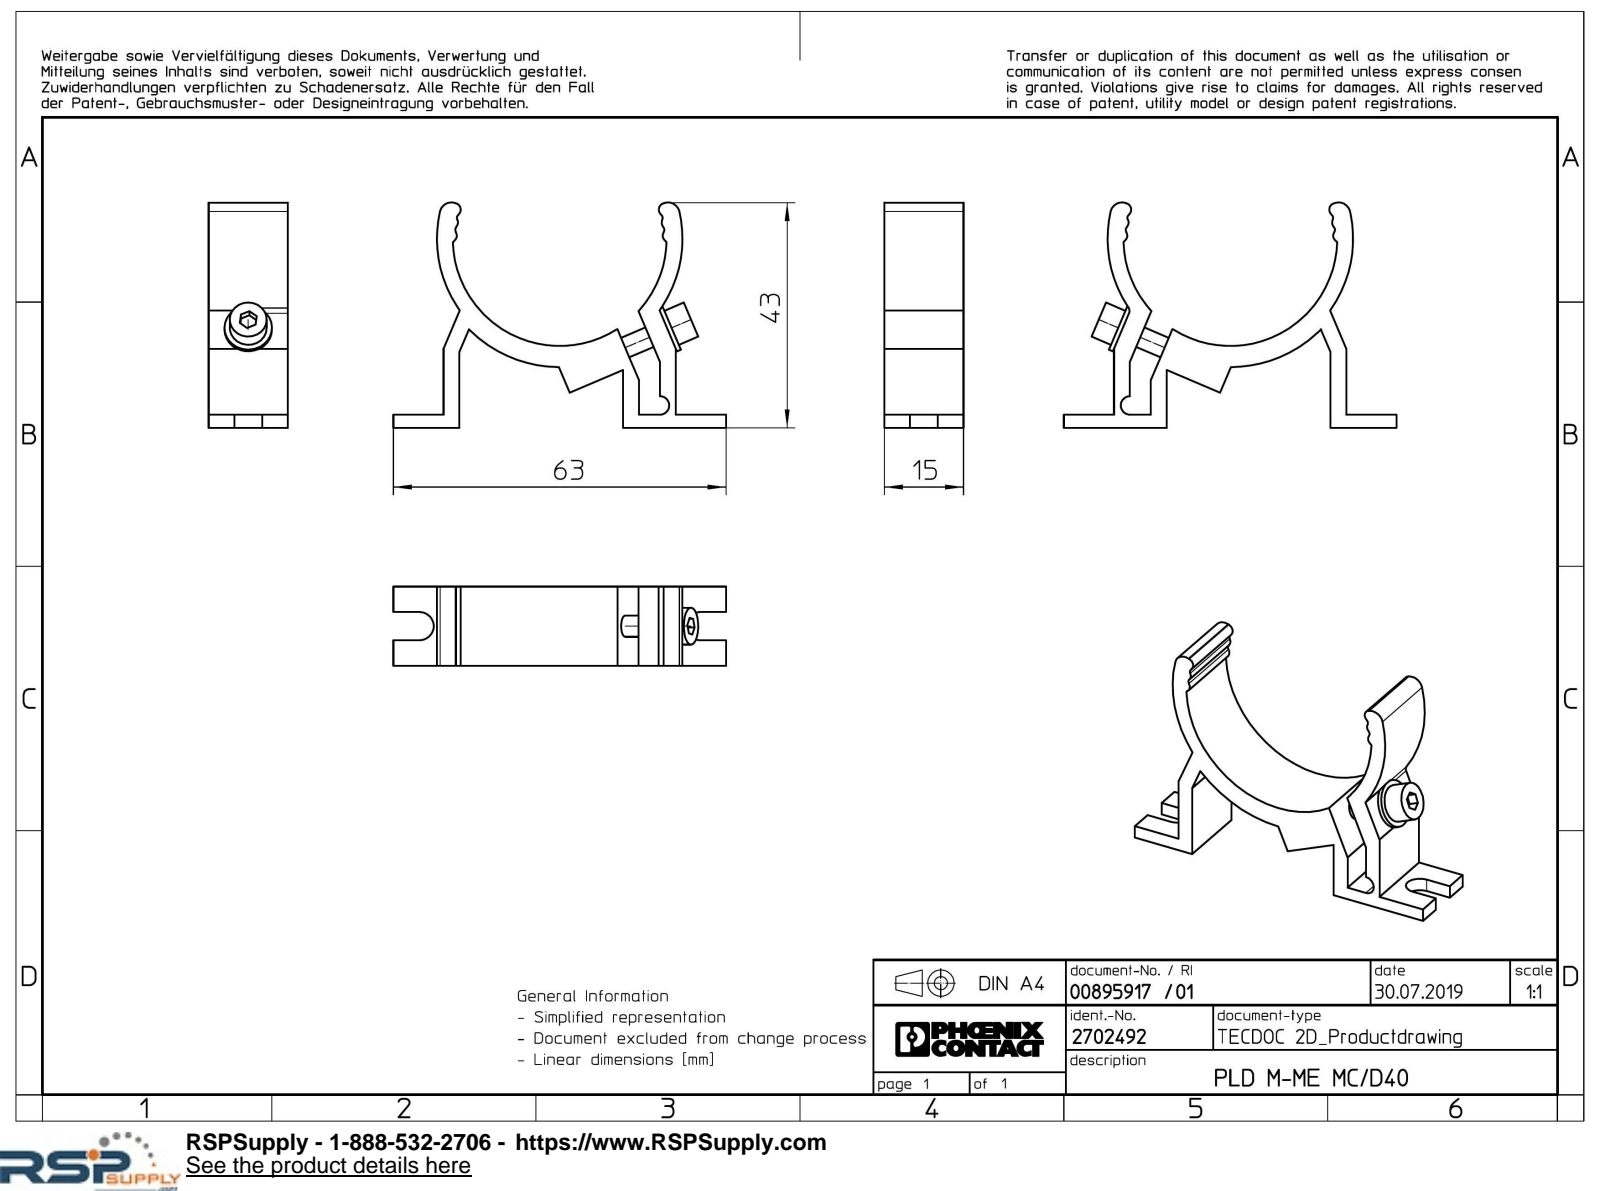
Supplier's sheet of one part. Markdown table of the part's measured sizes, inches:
| quantity | value |
| --- | --- |
| part name | PLD_M_ME_MC_D40-select |
| STEP written by | Creo Elements/Direct Modeling 20.1A 29-Sep-2018 (C) Parametric Technology GmbH (AUTOMOTIVE_DESIGN) |
| units | inches |
| bodies | 1 solid, 72 faces (42 planar, 30 cylindrical, 0 other) |
| overall size | 2.48 × 1.679 × 0.591 |
| volume | 0.495 in³ |
| surface area | 9.543 in² |
| round holes (diameter × count) | 0.185 × 1 |
| round bosses / shafts (diameter × count) | 0.354 × 1, 0.276 × 1, 0.157 × 1 |
| partial cylindrical surfaces (radius × count) | 0.049 × 6, 0.03 × 4, 0.012 × 2, 0.087 × 2, 0.104 × 2, 0.039 × 1, 0.069 × 1, 0.797 × 1 |
| main face-to-face distances | 0.591, 0.118, 1.614, 0.098, 1.339, 0.276, 1.732, 1.22, 0.394, 0.197 |
